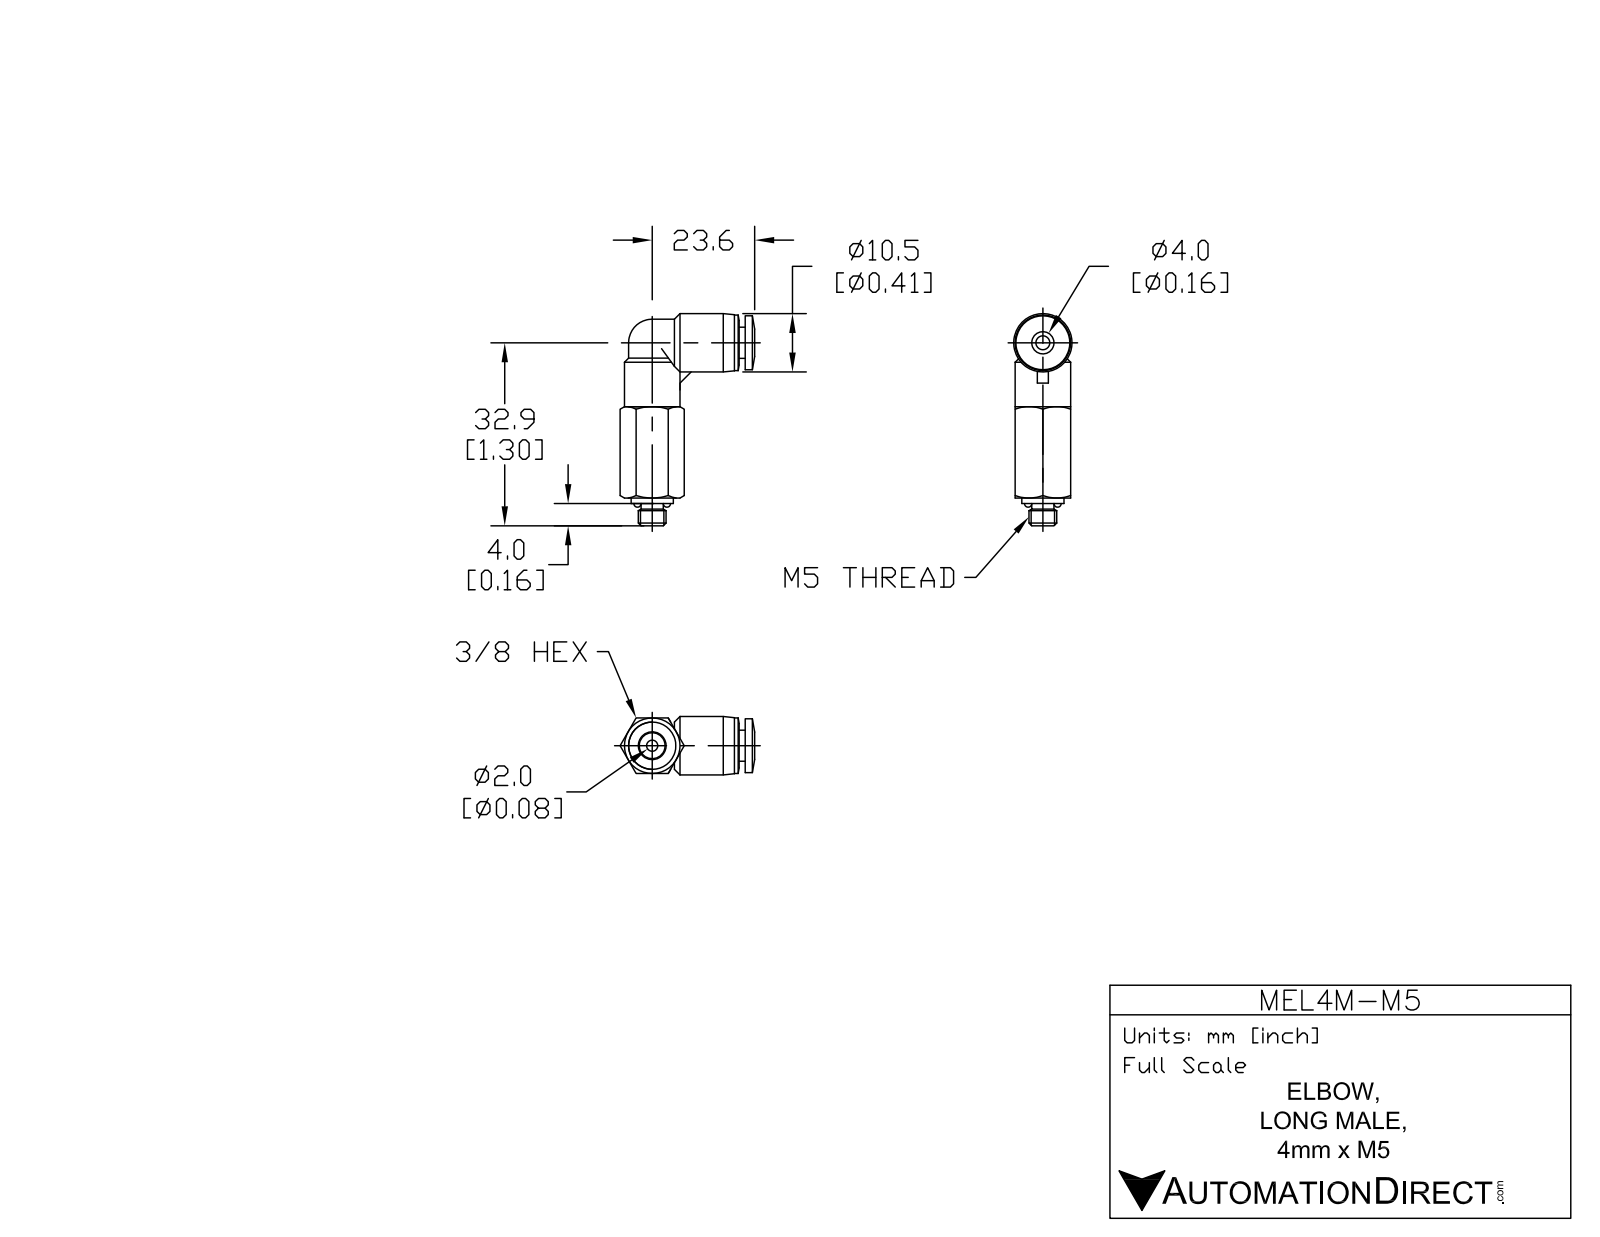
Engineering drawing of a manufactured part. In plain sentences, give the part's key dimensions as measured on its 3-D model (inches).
The part is named "MEL4M-M5". Its 3-D file was written by "SolidWorks 2018 (AUTOMOTIVE_DESIGN)". It is 1 solid with 78 faces: 18 planar, 25 cylindrical and 35 other. Overall it measures 1.506 by 0.954 by 0.413 inches. Its volume is 0.201 cubic inches and its surface area 3.615 square inches. Round holes: 2 of diameter 0.098, 1 of diameter 0.169. Round bosses or shafts: 2 of diameter 0.394, 1 of diameter 0.413, 1 of diameter 0.382, 1 of diameter 0.299, 1 of diameter 0.22, 1 of diameter 0.197, 1 of diameter 0.157. Partial cylindrical surfaces (rounded edges, fillets, slot ends): 2 of radius 0.167. The main face-to-face distances are 0.394, 0.043, 0.472, 0.516, 0.217, 0.193, 0.024, 0.161, 0.031, 0.055.
